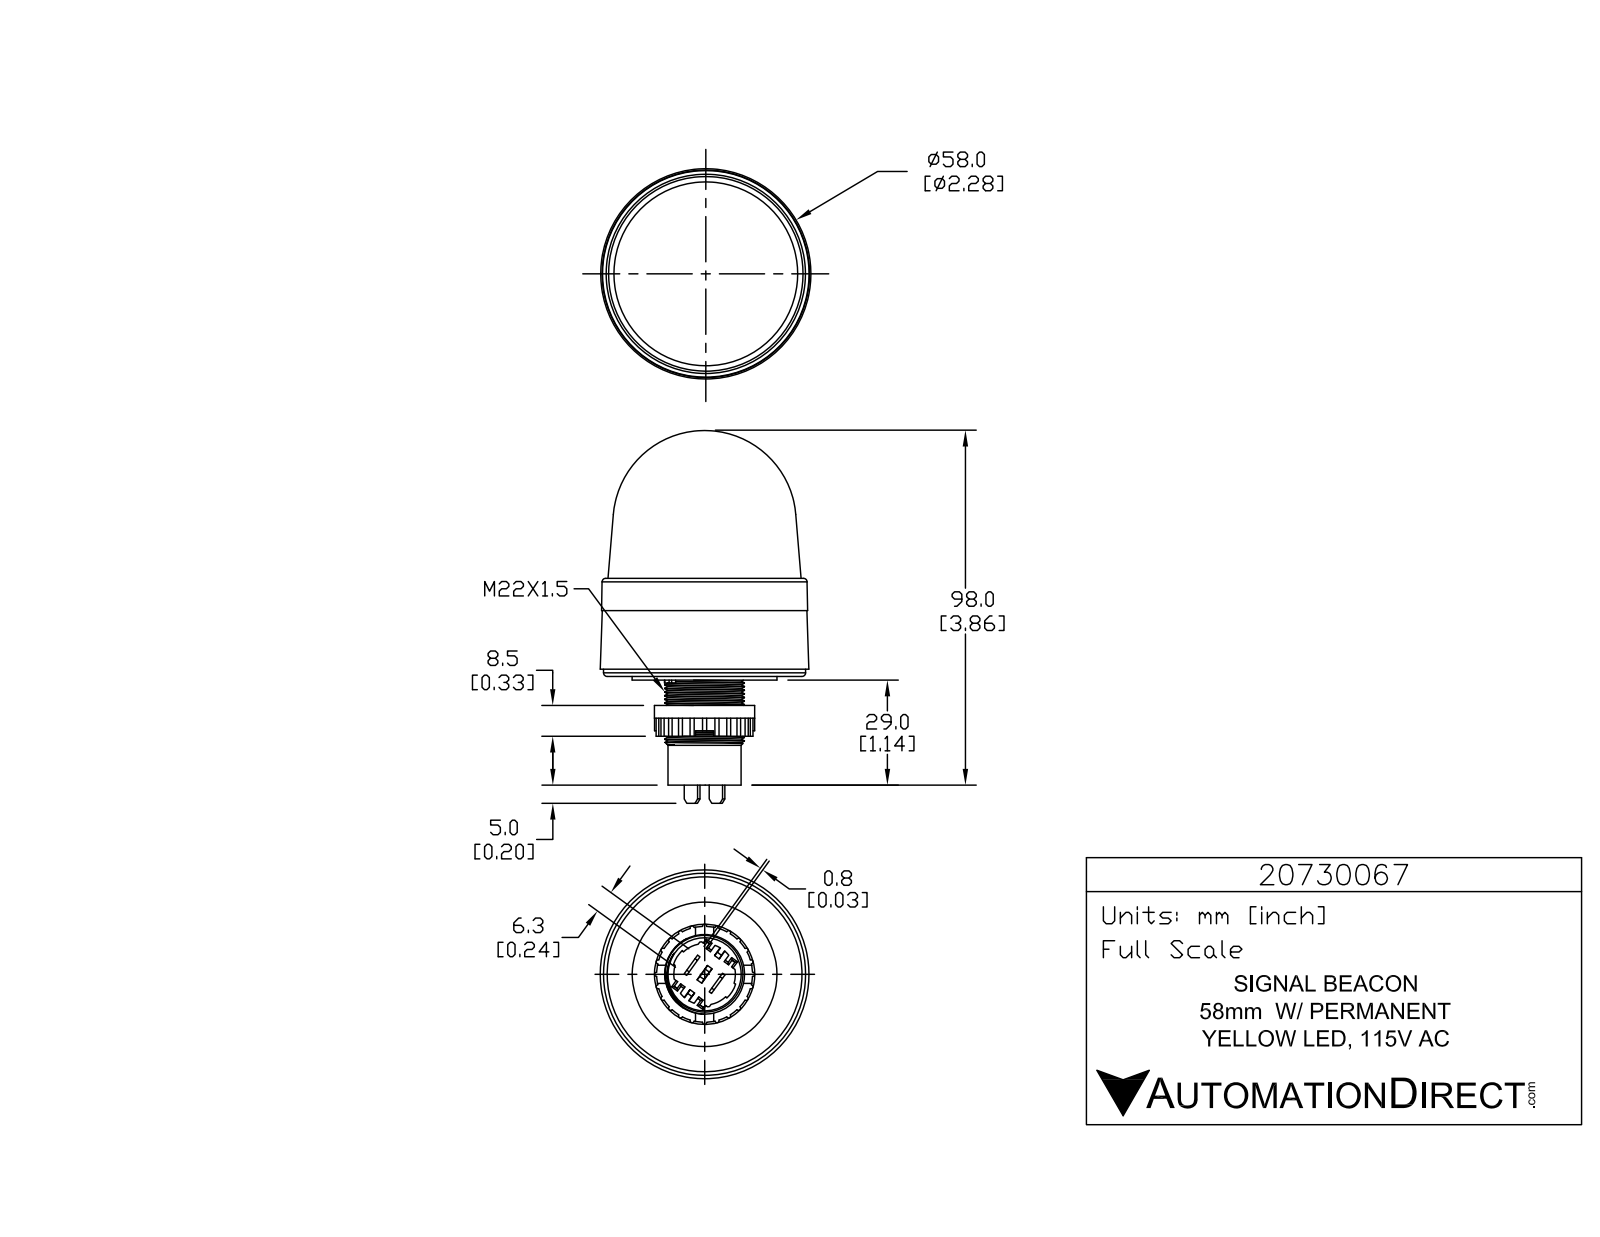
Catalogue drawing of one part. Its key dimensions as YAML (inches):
part_name: "20730067"
step_written_by: "SolidWorks 2015 (AUTOMOTIVE_DESIGN)"
units: inches
bodies: {solids: 1, faces: 266, planar: 119, cylindrical: 120, other: 27}
overall_size: [4.051, 2.269, 2.269]
volume: 9.016
surface_area: 31.05
round_holes:
  - {diameter: 0.906, count: 1}
round_bosses_or_shafts:
  - {diameter: 2.197, count: 1}
  - {diameter: 1.575, count: 1}
  - {diameter: 1.091, count: 1}
  - {diameter: 0.866, count: 1}
  - {diameter: 0.795, count: 1}
partial_cylinders:
  - {radius: 0.023, count: 24}
  - {radius: 0.02, count: 2}
  - {radius: 0.335, count: 1}
  - {radius: 0.354, count: 1}
  - {radius: 0.522, count: 1}
face_to_face_distances: [0.039, 0.276, 0.118, 1.142, 0.335, 0.315, 1.063, 0.748, 1.024, 0.728]
